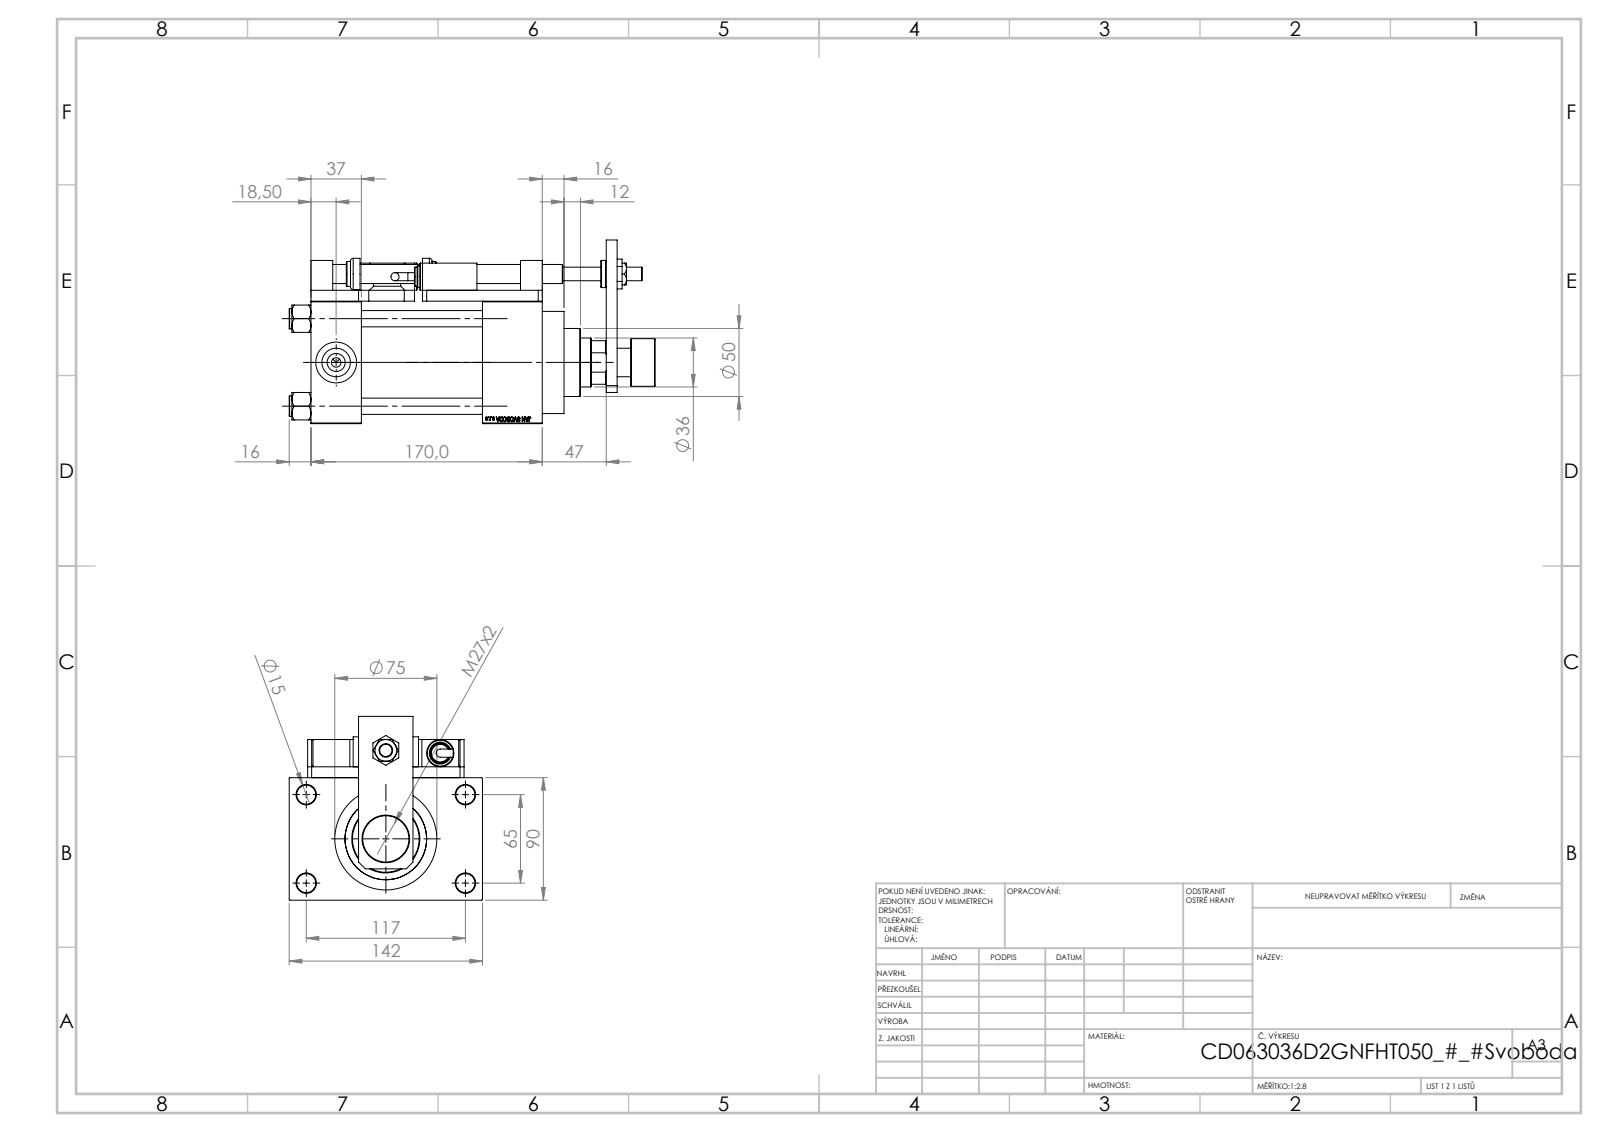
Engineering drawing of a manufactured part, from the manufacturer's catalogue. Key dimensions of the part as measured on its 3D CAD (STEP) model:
Part name (STEP PRODUCT): V215CD_SWITCH_Q_SWITCH; V215CD_VC_A; V215CD_SWITCH_Q_TYC; V215CD_SWITCH_Q_PODLOZKA_FRONT (+7 more)
STEP written by: SolidWorks 2019 (CONFIG_CONTROL_DESIGN)
Units: millimetres
Bodies: 26 solids, 1398 faces (646 planar, 167 cylindrical, 585 other)
Overall size (bounding box): 269 × 142 × 135
Volume: 1 463 000 mm³ · Surface area: 320 700 mm²
Round holes (diameter × count): ⌀14 ×5, ⌀8.5 ×4, ⌀12 ×4, ⌀13.5 ×4, ⌀7 ×3, ⌀20.96 ×3, ⌀30 ×3, ⌀10 ×1, ⌀25.5 ×1, ⌀27 ×1, ⌀36 ×1, ⌀39 ×1
Round bosses / shafts (diameter × count): ⌀15 ×4, ⌀20 ×3, ⌀16 ×2, ⌀14 ×2, ⌀6 ×2, ⌀75 ×1, ⌀69 ×1, ⌀35 ×1
Partial cylindrical surfaces — rounded edges, fillets, slot ends (radius × count): R7.5 ×4
Main face-to-face distances: 8, 90, 44, 37, 170, 98, 133, 89, 126, 47
Hole centre spacings: 66.92, 26.35, 45.47, 64.3, 69.81, 90.65, 111.34, 65
